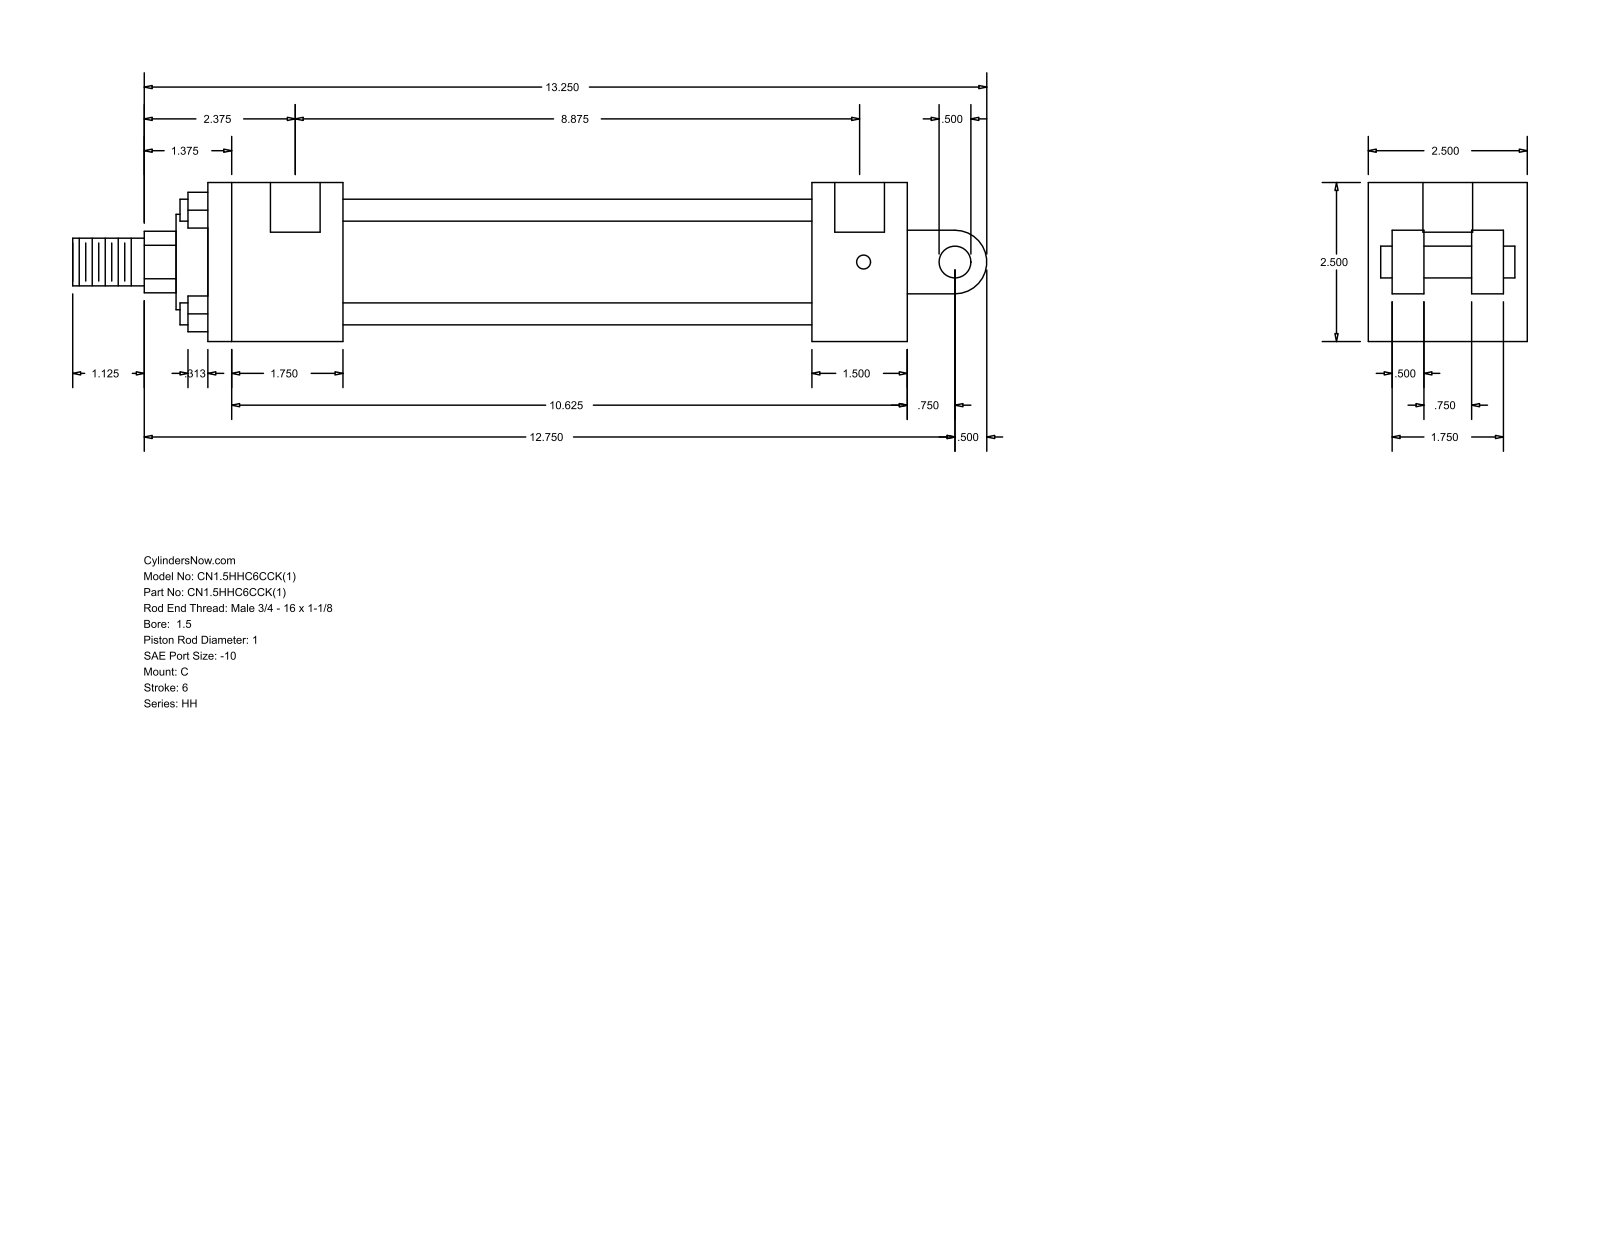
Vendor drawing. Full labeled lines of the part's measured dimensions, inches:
Part name (STEP PRODUCT): HH_C__0150_1
STEP written by: GSSL Pune (CONFIG_CONTROL_DESIGN)
Units: inches
Bodies: 0 solids, 99 faces (70 planar, 29 cylindrical, 0 other)
Overall size (bounding box): 14.375 × 2.5 × 2.5
Round holes (diameter × count): ⌀0.219 ×4, ⌀0.781 ×2
Round bosses / shafts (diameter × count): ⌀0.345 ×4, ⌀1.75 ×1, ⌀1.5 ×1, ⌀1 ×1, ⌀0.75 ×1, ⌀0.5 ×1
Partial cylindrical surfaces — rounded edges, fillets, slot ends (radius × count): R0.484 ×1, R0.5 ×1
Main face-to-face distances: 2.5, 2.125, 1.5, 7.375, 8.875, 9.5, 11, 0.5, 0.875, 1.625
Hole centre spacings: 0.063, 8.937, 9, 8.875
